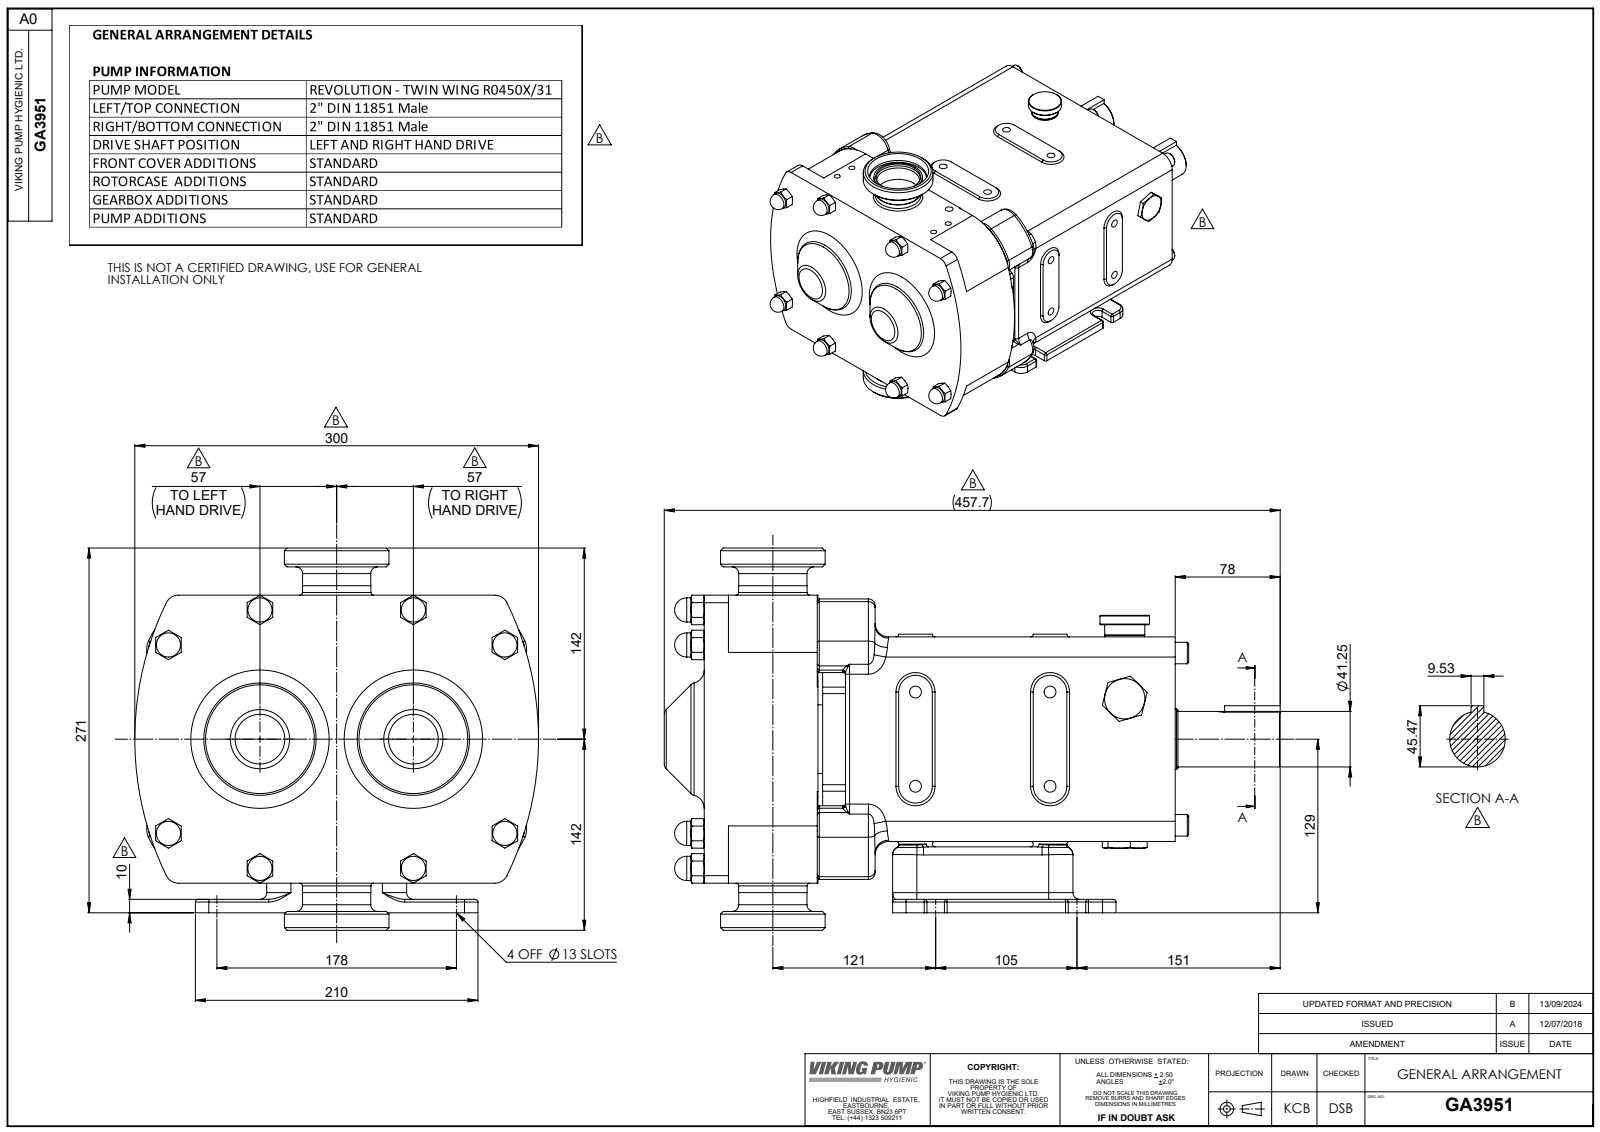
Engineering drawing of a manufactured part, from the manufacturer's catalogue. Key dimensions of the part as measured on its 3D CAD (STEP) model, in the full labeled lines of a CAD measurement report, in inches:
Part name (STEP PRODUCT): Copy of Z94-5031-33 - 2 INCH DIN11851^GA3951; GA3951; Copy of R0450 CPP V LHD^GA3951
STEP written by: SolidWorks 2023 (AUTOMOTIVE_DESIGN)
Units: inches
Bodies: 3 solids, 960 faces (301 planar, 293 cylindrical, 366 other)
Overall size (bounding box): 18.02 × 11.811 × 11.181
Volume: 1 023 in³ · Surface area: 1 071 in²
Round holes (diameter × count): ⌀0.346 ×8, ⌀0.268 ×4, ⌀0.339 ×2, ⌀1.331 ×1, ⌀1.874 ×1, ⌀1.969 ×1, ⌀2.508 ×1
Round bosses / shafts (diameter × count): ⌀0.709 ×8, ⌀0.63 ×6, ⌀1.772 ×2, ⌀1.624 ×2, ⌀3.059 ×1, ⌀2.126 ×1, ⌀2.008 ×1, ⌀2.004 ×1
Partial cylindrical surfaces — rounded edges, fillets, slot ends (radius × count): R0.079 ×38, R0.394 ×30, R0.197 ×19, R0.232 ×8, R0.591 ×8, R0.709 ×8, R0.118 ×4, R0.236 ×4
Main face-to-face distances: 5.984, 3.327, 10.453, 13.78, 3.465, 10.315, 0.138, 10.472, 1.693, 0.394
Hole centre spacings: 2.756, 3.937, 4.806, 0.906, 1.1, 1.869, 2.427, 2.994
